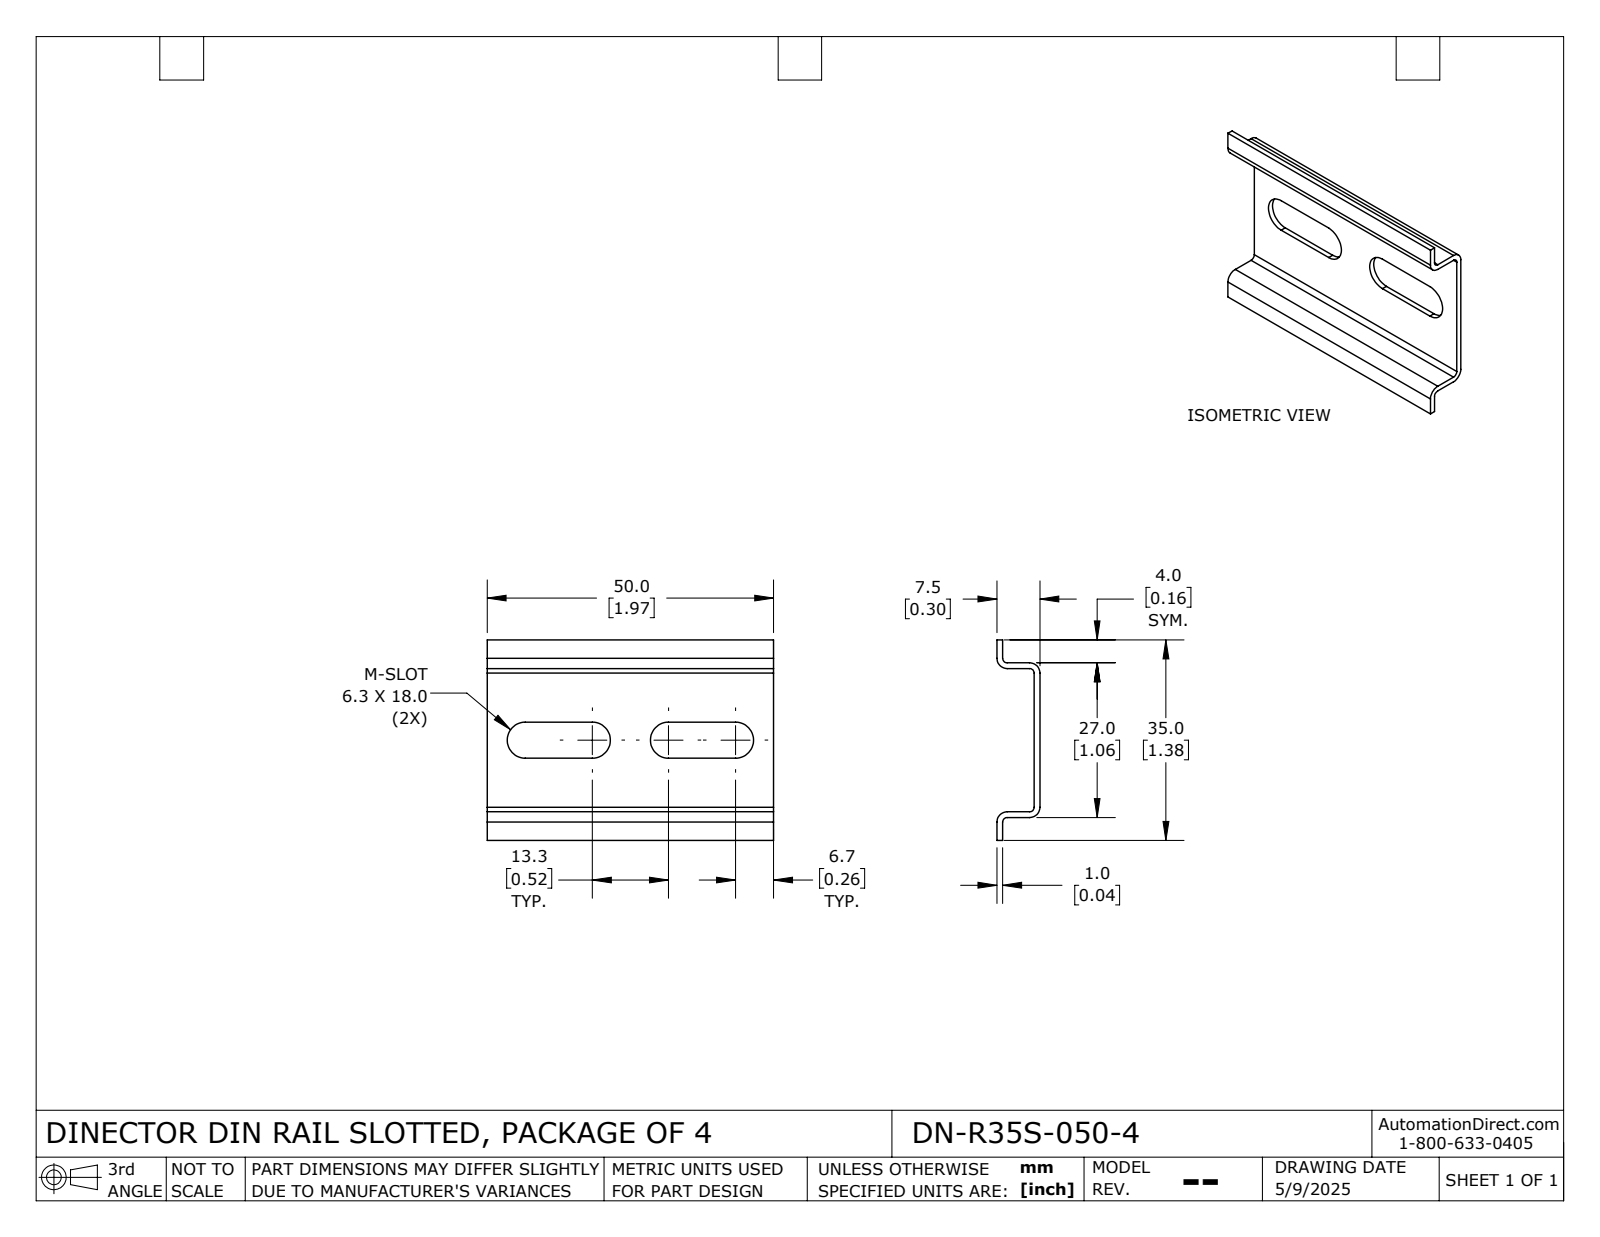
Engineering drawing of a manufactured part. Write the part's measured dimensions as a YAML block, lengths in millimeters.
part_name: "DN-R35S-050-4"
step_written_by: "SolidWorks 2024 (AUTOMOTIVE_DESIGN)"
units: millimeters
bodies: {solids: 1, faces: 30, planar: 18, cylindrical: 12, other: 0}
overall_size: [50, 35, 7.5]
volume: 2079
surface_area: 4435
partial_cylinders:
  - {radius: 0.8, count: 4}
  - {radius: 1.8, count: 4}
  - {radius: 3.15, count: 4}
face_to_face_distances: [1, 6.5, 26, 7.5, 5.5, 27, 25, 4, 5, 30]
